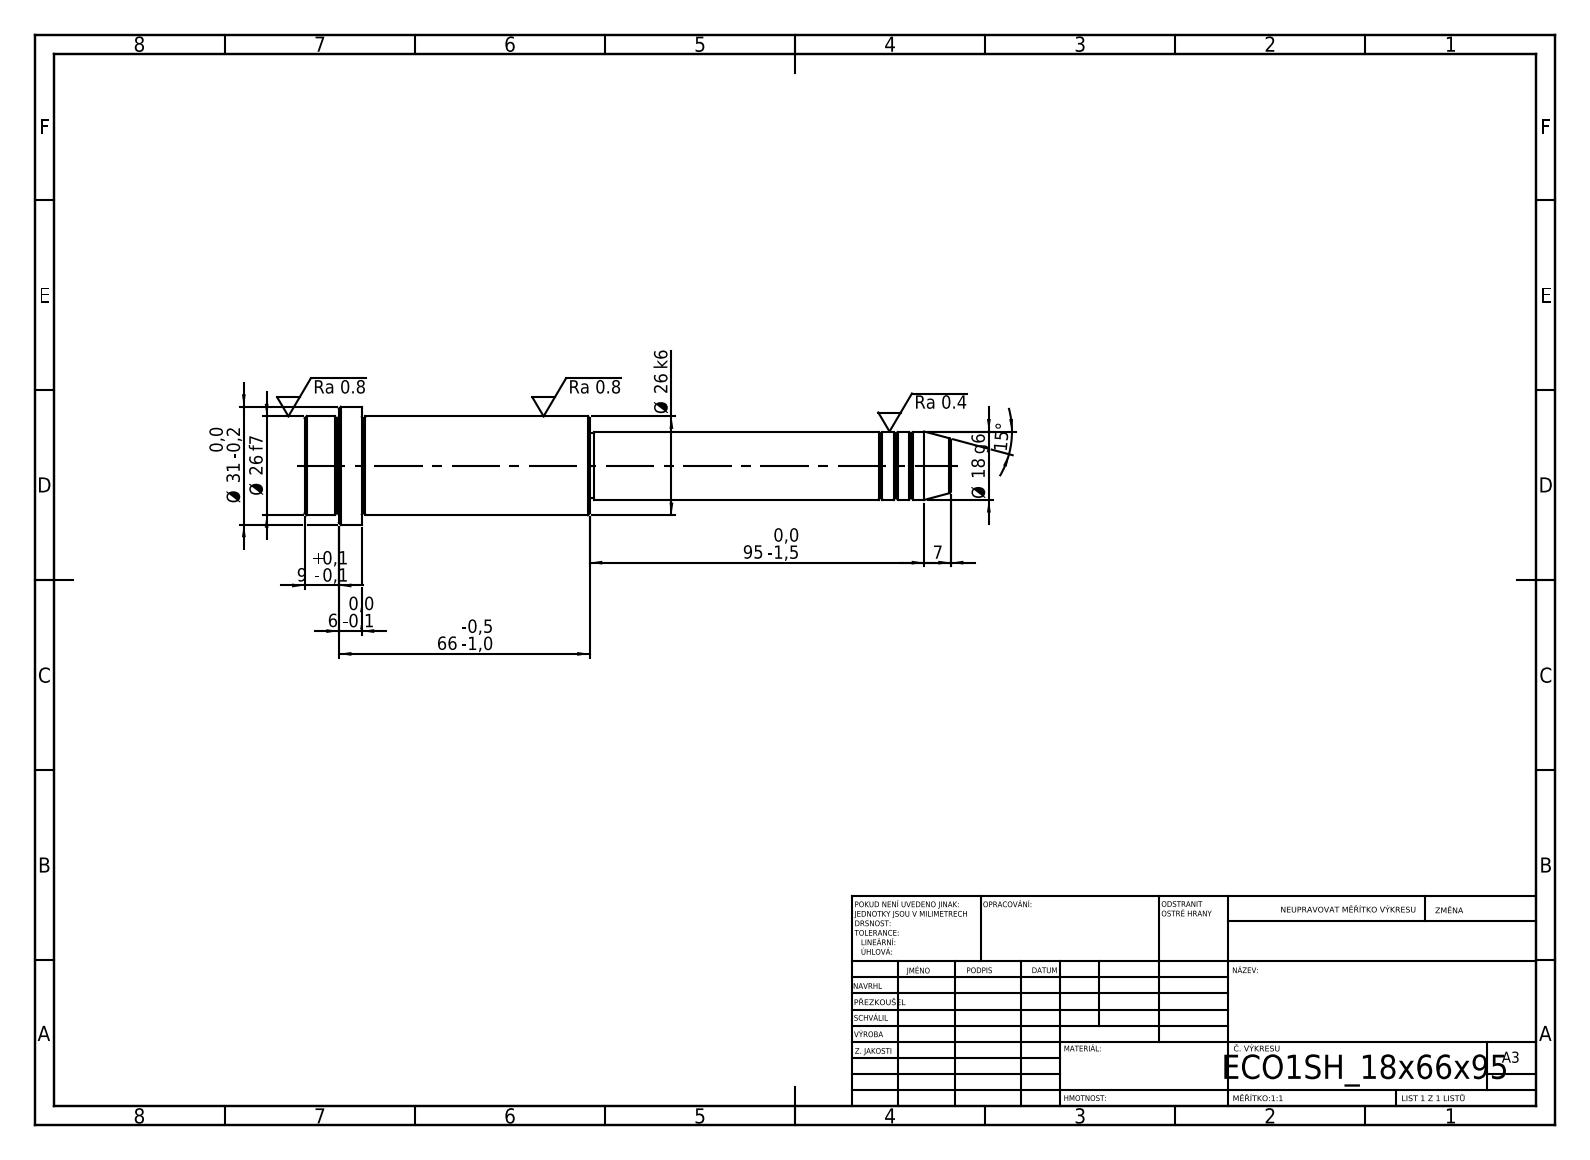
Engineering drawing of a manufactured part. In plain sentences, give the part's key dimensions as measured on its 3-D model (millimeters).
Its 3-D file was written by "SolidWorks 2019 (CONFIG_CONTROL_DESIGN)". It is 1 solid with 52 faces: 6 planar, 16 cylindrical and 30 other. Overall it measures 170 by 31 by 31 millimeters. Its volume is 64 803 cubic millimeters and its surface area 13 122 square millimeters. Round bosses or shafts: 1 of diameter 31, 1 of diameter 26, 1 of diameter 18, 1 of diameter 17. The main face-to-face distances are 75, 60, 15, 66, 6, 9, 95, 155, 161, 170.
